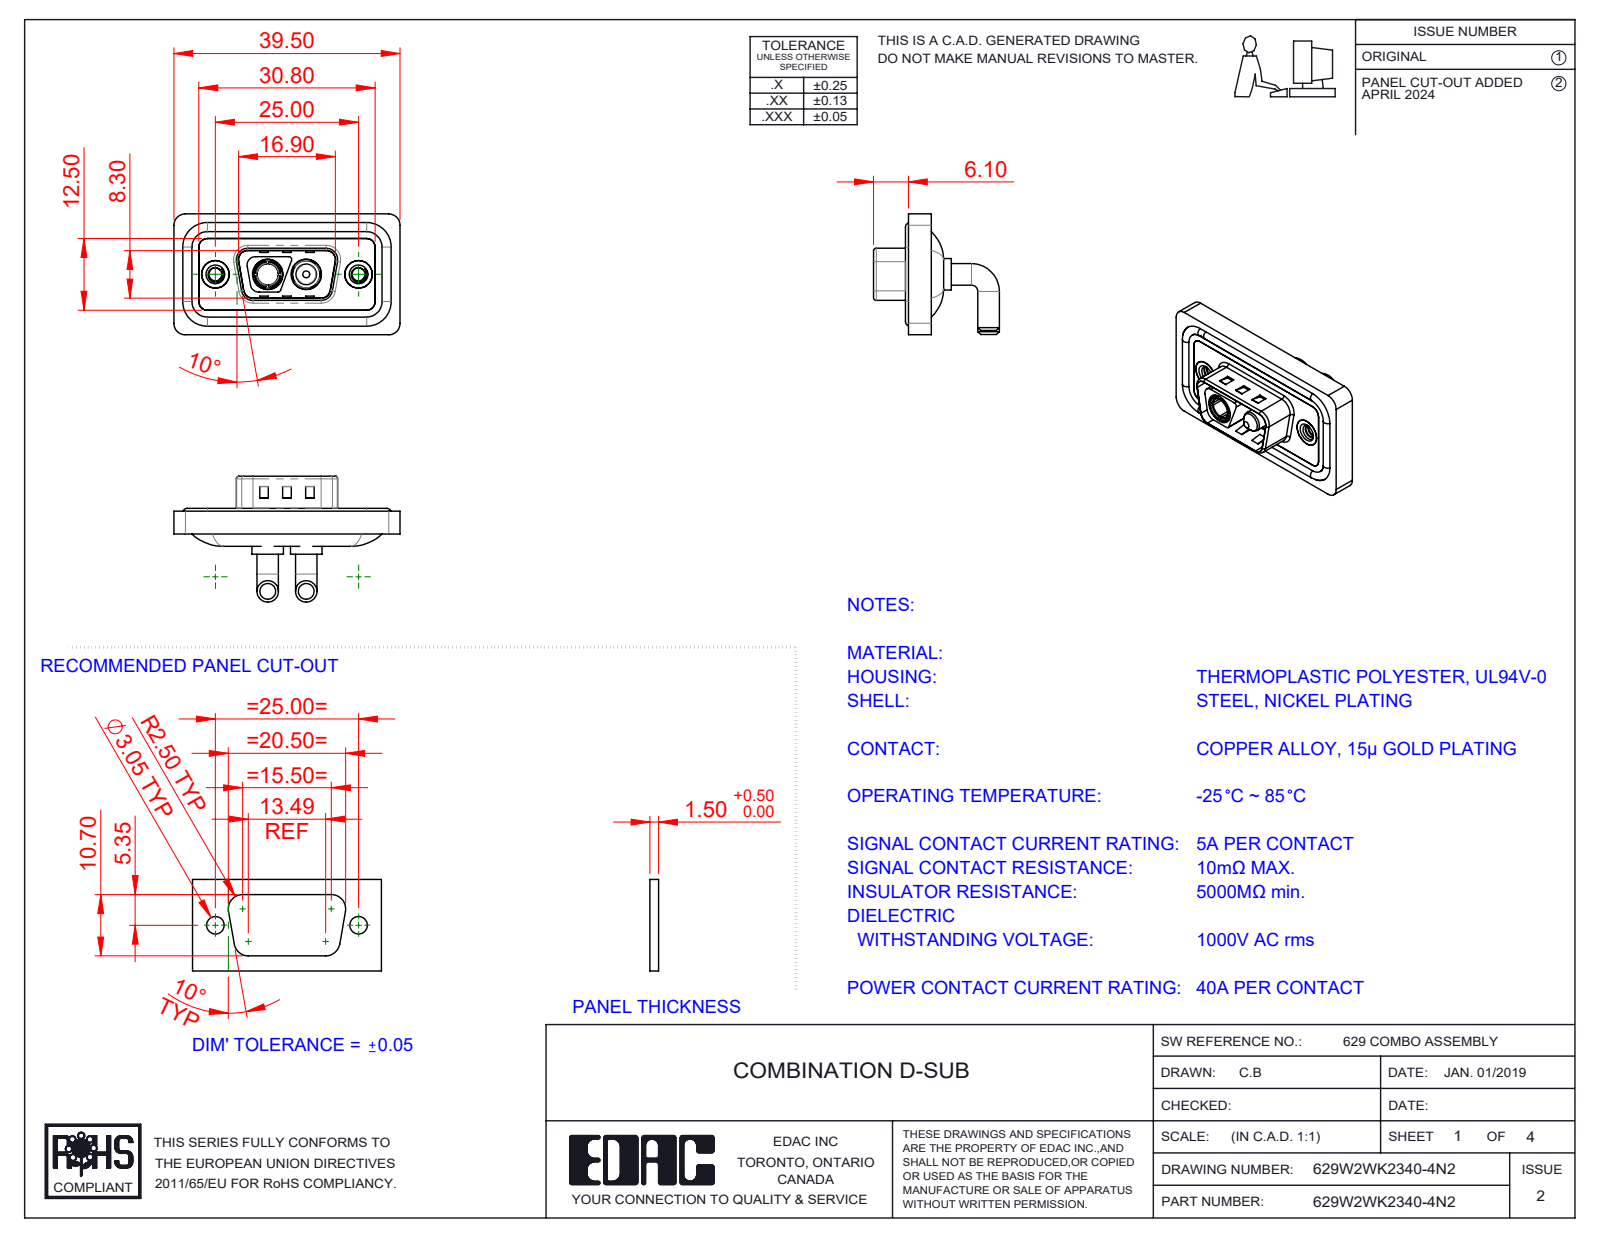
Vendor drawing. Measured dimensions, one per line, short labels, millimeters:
name: 629Combo Shell Rear_09 Contacts; Power Pin_40A RA; Power Socket_40A RA; 629Combo Shell Front_09 Contacts (+4 more)
written by: SolidWorks 2023 (CONFIG_CONTROL_DESIGN)
unit: mm
bodies: 11 solids, 542 faces (189 planar, 231 cylindrical, 122 other)
size: 39.5 × 21.98 × 21.1
volume: 4 842 mm³; area: 7 622 mm²
holes: 2× ⌀2.26, 2× ⌀4, 2× ⌀4.8, 2× ⌀4.85, 2× ⌀5, 2× ⌀5.3, 1× ⌀3.7
bosses: 4× ⌀3.75, 4× ⌀1.6, 2× ⌀5.5, 2× ⌀5.2, 2× ⌀4.9, 2× ⌀4.75, 1× ⌀4.96, 1× ⌀3.6
rounds: 20× R1.5, 18× R2, 10× R0.5, 8× R1.6, 4× R0.25, 4× R0.6, 4× R0.65, 4× R0.9
face distances: 0.4, 2.9, 1.1, 0.8, 2.1, 2.5, 3.1, 1.6, 4.5, 1.5
hole spacings: 9.14, 15.86, 6.72, 25
